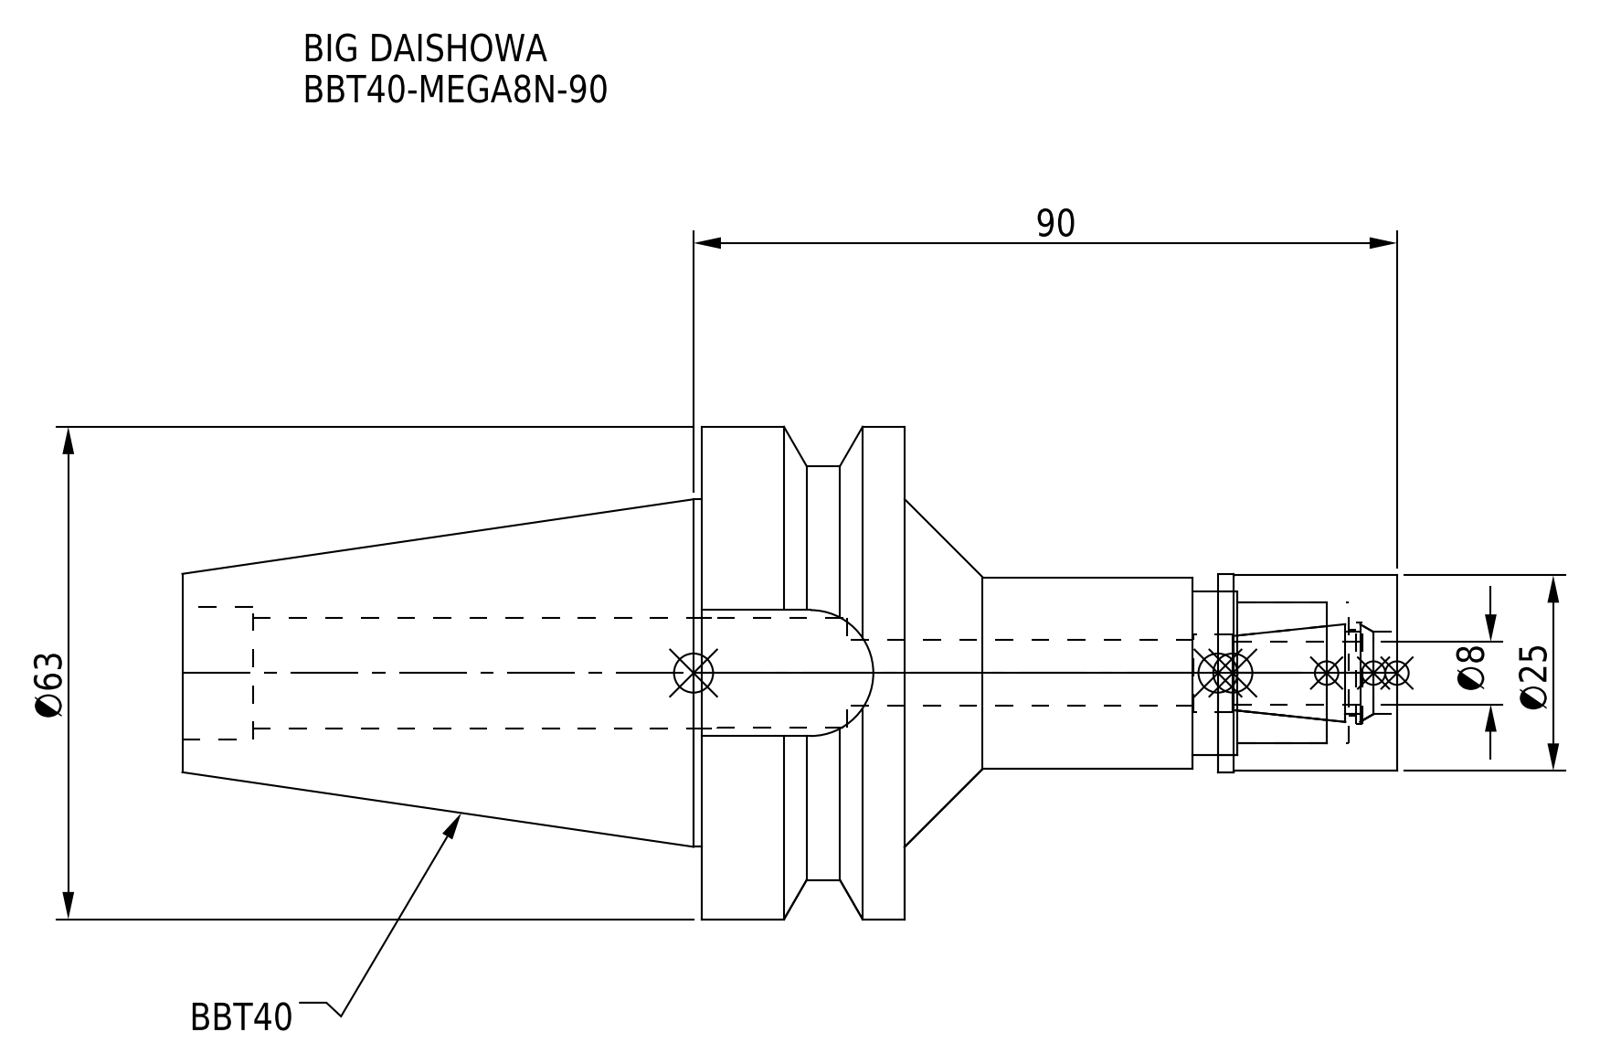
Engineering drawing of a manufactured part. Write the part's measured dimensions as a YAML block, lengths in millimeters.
part_name: "BBT40MN08090-080_ASM.stp; MGN8_1.stp; BBT40-MEGA8N-90-080-FreeParts; BBT40-MEGA8N-90_1.stp (+3 more)"
step_written_by: "SolidWorks 2019 (CONFIG_CONTROL_DESIGN)"
units: millimeters
bodies: {solids: 2, faces: 80, planar: 24, cylindrical: 42, other: 14}
overall_size: [155.4, 63, 63]
volume: 150974
surface_area: 31673
round_holes:
  - {diameter: 8.4, count: 1}
  - {diameter: 10, count: 1}
  - {diameter: 10.5, count: 1}
  - {diameter: 11, count: 1}
  - {diameter: 13, count: 1}
  - {diameter: 14, count: 1}
  - {diameter: 14.1, count: 1}
  - {diameter: 14.2, count: 1}
  - {diameter: 17, count: 1}
  - {diameter: 18, count: 1}
  - {diameter: 21, count: 1}
round_bosses_or_shafts:
  - {diameter: 63, count: 1}
  - {diameter: 53, count: 1}
  - {diameter: 44.45, count: 1}
  - {diameter: 25.3, count: 1}
  - {diameter: 25, count: 1}
  - {diameter: 24.5, count: 1}
partial_cylinders:
  - {radius: 8.05, count: 1}
face_to_face_distances: [26, 63, 89, 45, 155.4, 92.4, 66.4, 9, 146.4, 16.1]
